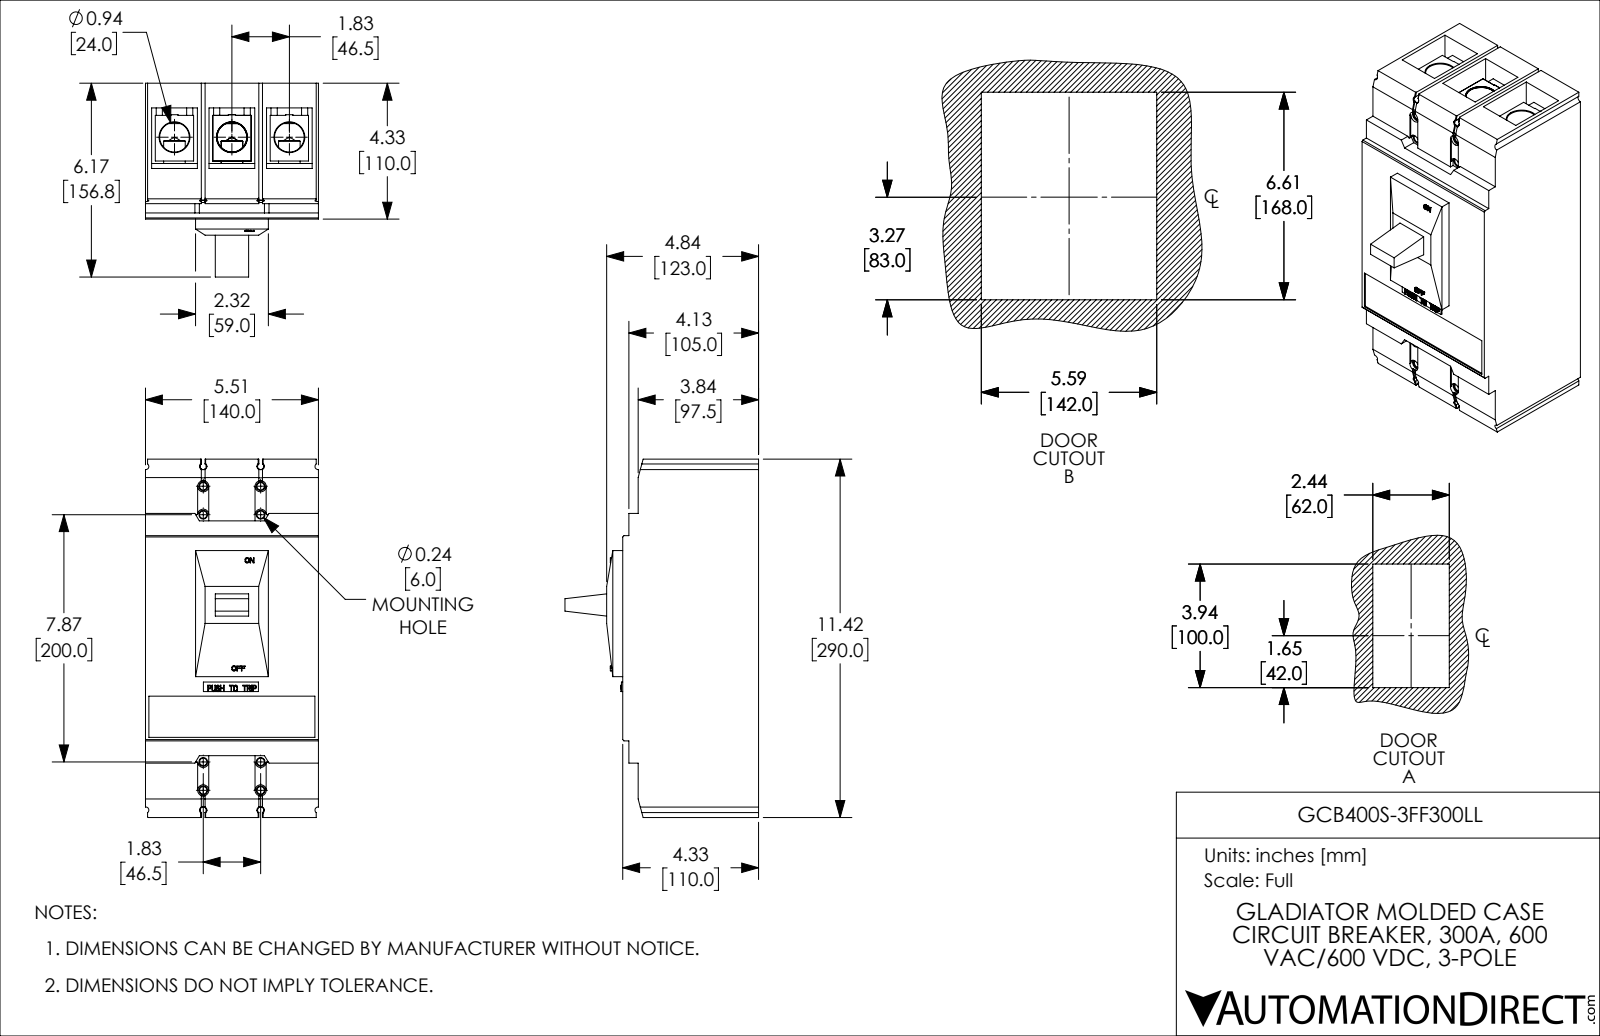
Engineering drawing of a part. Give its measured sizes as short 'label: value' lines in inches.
name: GCB400S-3FF300LL
written by: SolidWorks 2021 (CONFIG_CONTROL_DESIGN)
unit: in
bodies: 26 solids, 1319 faces (935 planar, 200 cylindrical, 184 other)
size: 11.417 × 6.173 × 5.512
volume: 245.8 in³; area: 525.8 in²
holes: 8× ⌀0.236, 6× ⌀0.413, 6× ⌀0.594, 6× ⌀0.688, 4× ⌀0.197, 4× ⌀0.354, 3× ⌀0.945
bosses: 6× ⌀0.575, 6× ⌀0.394, 1× ⌀0.75
rounds: 28× R0.098, 8× R0.039, 4× R0.177
face distances: 1.831, 5.512, 0.492, 1.457, 0.118, 1.339, 1.772, 1.713, 1.949, 0.197
hole spacings: 1.831, 0.968, 1.089, 1.316, 8.514, 9.415, 10.042, 0.63
